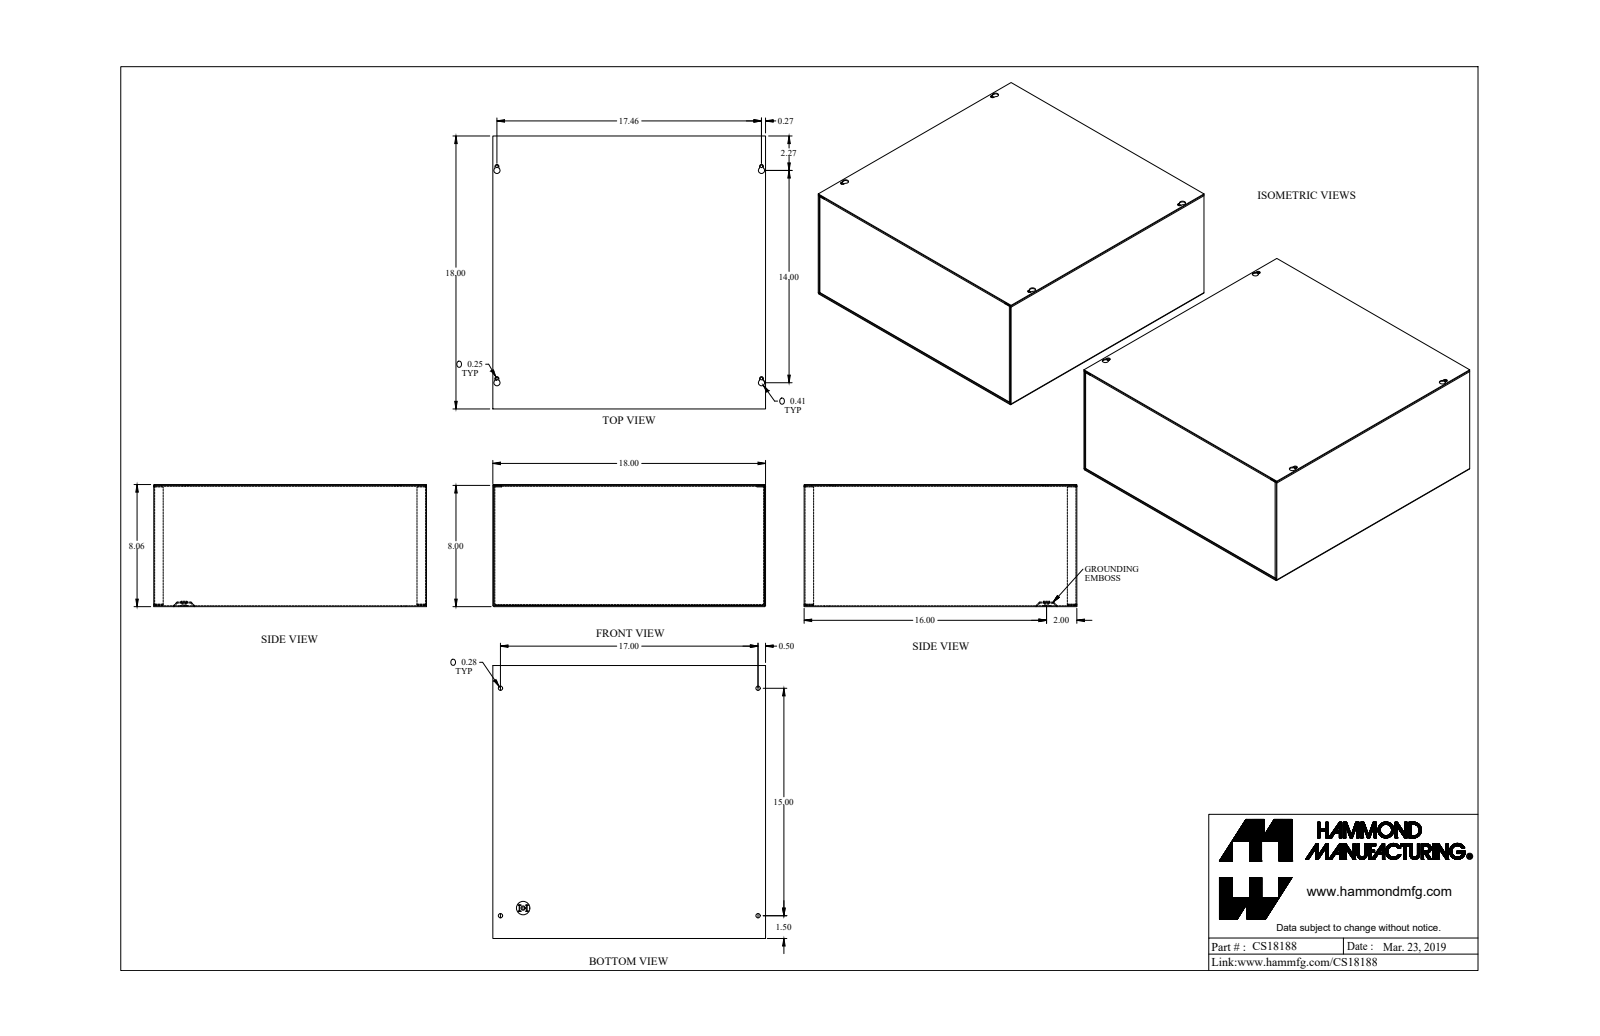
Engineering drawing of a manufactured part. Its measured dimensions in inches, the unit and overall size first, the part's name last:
Units: inches
Overall size (bounding box): 18 × 18 × 8.057
Round holes (diameter × count): ⌀0.17 ×5, ⌀0.281 ×4, ⌀0.5 ×1
Round bosses / shafts (diameter × count): ⌀0.492 ×1, ⌀0.284 ×1
Partial cylindrical surfaces — rounded edges, fillets, slot ends (radius × count): R0.029 ×12, R0.086 ×12, R0.057 ×8, R0.125 ×4, R0.203 ×4
Main face-to-face distances: 0.057, 8, 17.943, 7.943, 8.057, 18, 17.886, 0.08, 7.863, 7.92
Hole centre spacings: 0.55, 14.502, 17.237, 22.519, 14, 15, 17, 17.46
Volume: 72.98 in³ · Surface area: 2 578 in²
Bodies: 4 solids, 205 faces (125 planar, 72 cylindrical, 8 other)
Part name (STEP PRODUCT): CS18188_Default
STEP written by: SolidWorks 2019 (CONFIG_CONTROL_DESIGN)
